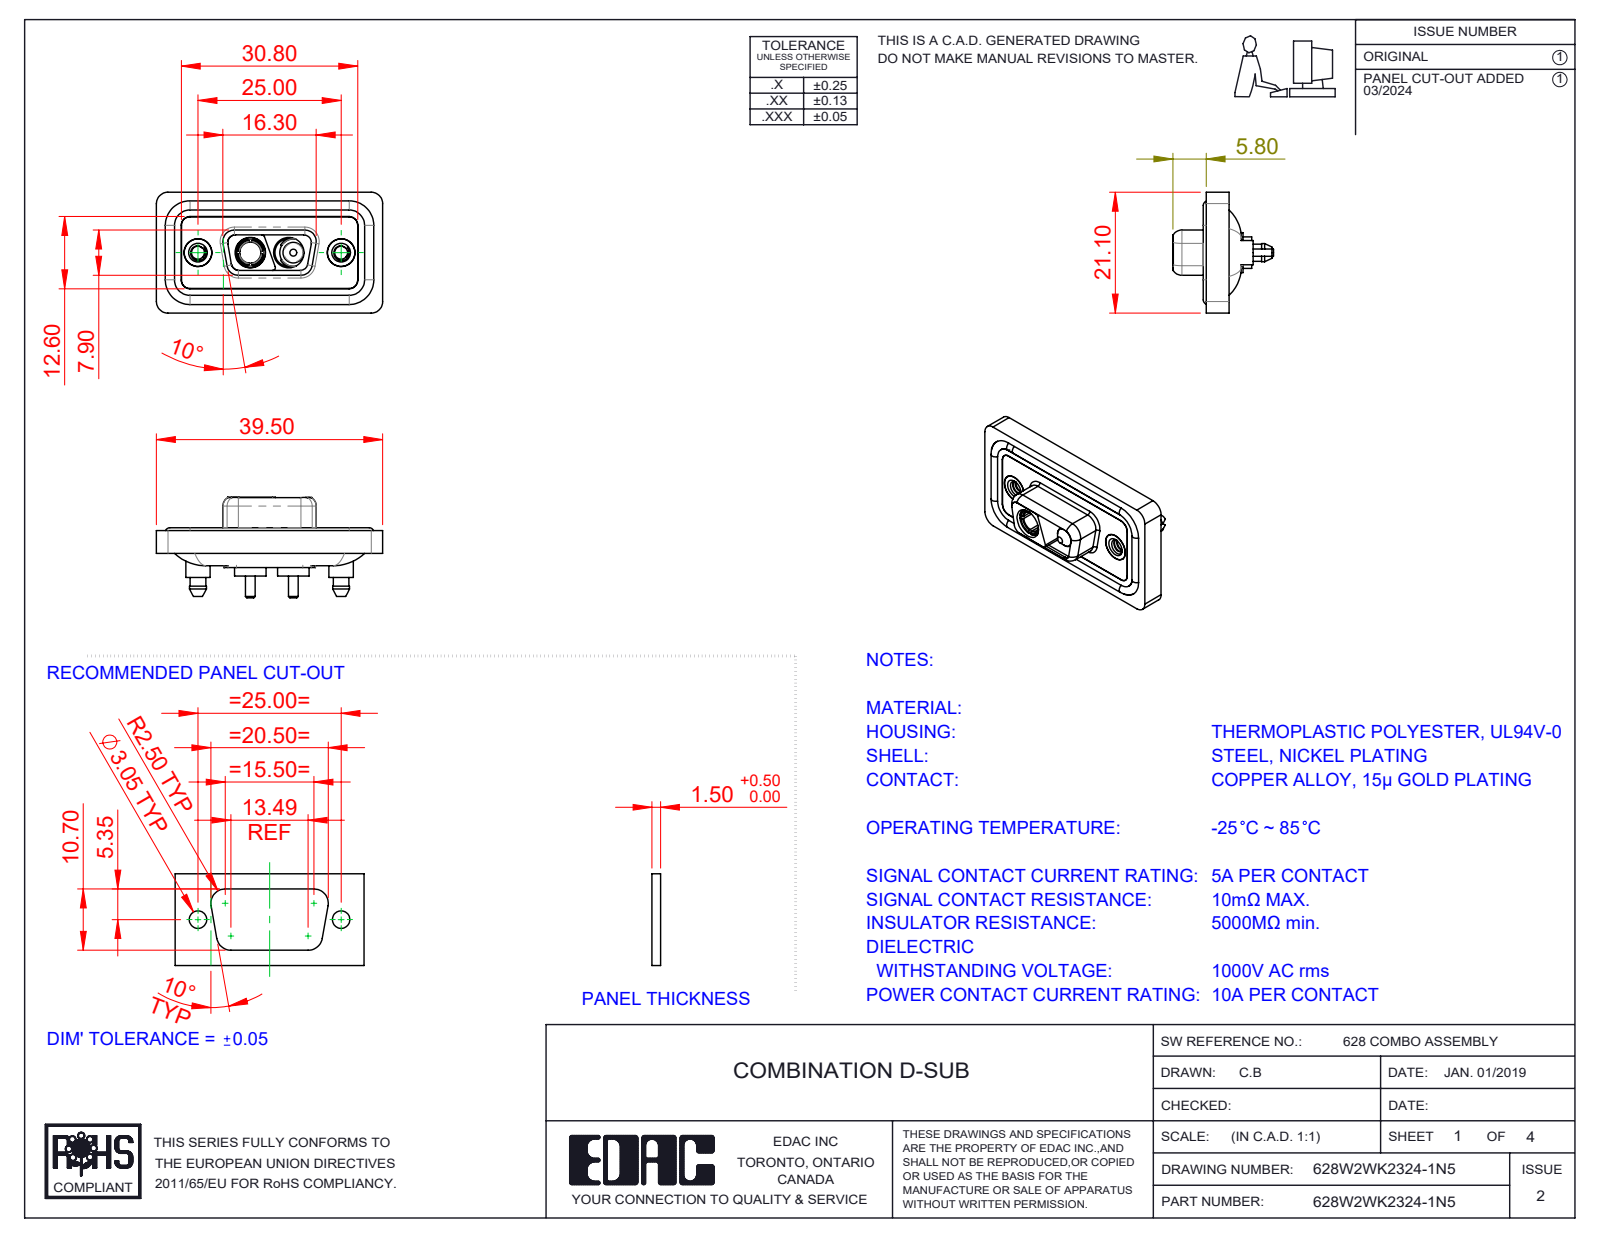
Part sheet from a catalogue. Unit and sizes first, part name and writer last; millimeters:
Units: millimetres
Overall size (bounding box): 39.5 × 21.1 × 17.55
Round holes (diameter × count): ⌀4.85 ×4, ⌀2.26 ×2, ⌀4 ×2, ⌀4.05 ×2, ⌀5 ×2, ⌀5.3 ×2, ⌀3.7 ×1
Round bosses / shafts (diameter × count): ⌀1.6 ×4, ⌀5.5 ×2, ⌀5.4 ×2, ⌀5.2 ×2, ⌀4.95 ×2, ⌀4.8 ×2, ⌀4.75 ×2, ⌀4.25 ×2
Partial cylindrical surfaces — rounded edges, fillets, slot ends (radius × count): R1.5 ×24, R2 ×18, R1.6 ×10, R1.35 ×8, R0.5 ×6, R0.25 ×4, R0.6 ×4, R0.65 ×4
Main face-to-face distances: 0.4, 1.1, 2.9, 1.6, 0.5, 1.8, 5.65, 1.5, 4, 5.35
Hole centre spacings: 9.14, 15.86, 6.72, 25
Volume: 4 707 mm³ · Surface area: 7 651 mm²
Bodies: 11 solids, 550 faces (160 planar, 263 cylindrical, 127 other)
Part name (STEP PRODUCT): 628Combo Shell Rear_09 Contacts; 628W2WK2324-1N5; Power Socket_10A S; 628Combo Shell Front_09 Contacts (+4 more)
STEP written by: SolidWorks 2023 (CONFIG_CONTROL_DESIGN)
